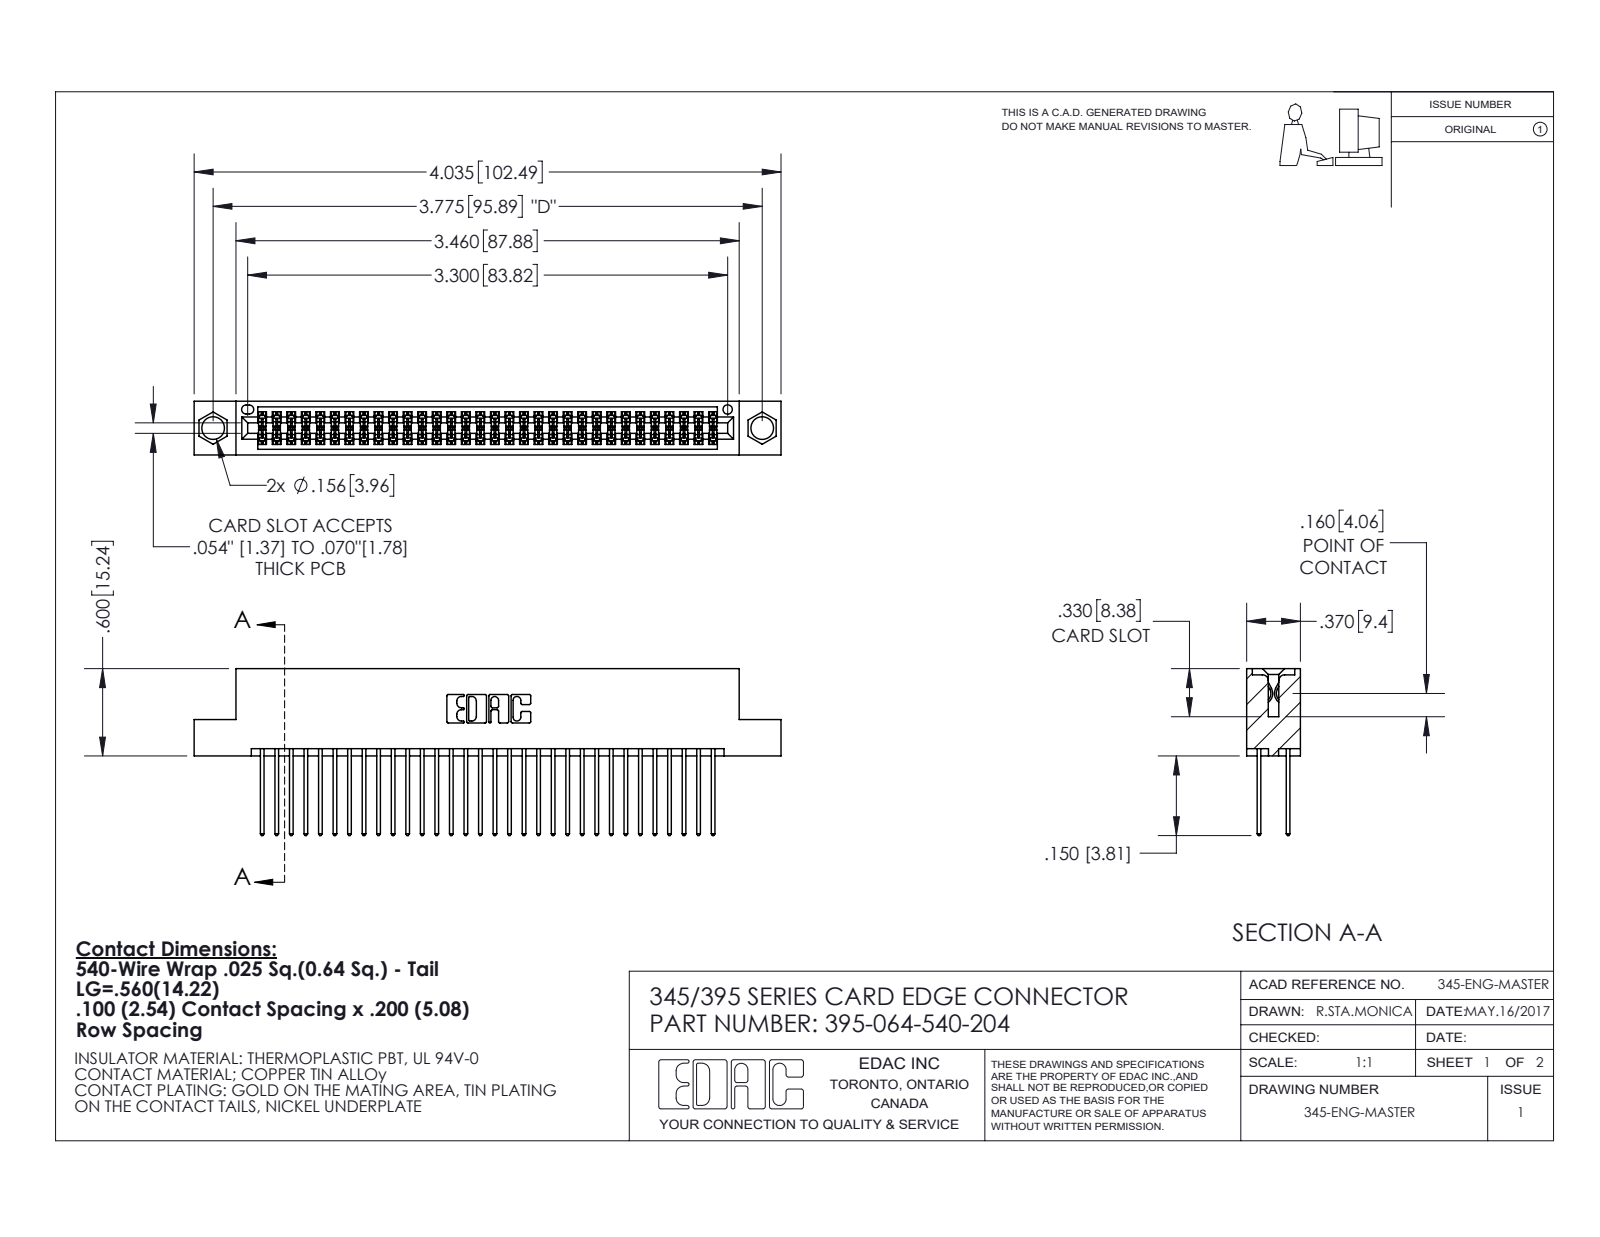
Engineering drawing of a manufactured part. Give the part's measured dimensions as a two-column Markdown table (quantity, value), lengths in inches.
| quantity | value |
| --- | --- |
| part name | 395-064-540-204; 345-292-001_345-293-140; 345 Part_Flush Mounting Lugs - 0.156 Dia-TI |
| STEP written by | SolidWorks 2020 (CONFIG_CONTROL_DESIGN) |
| units | inches |
| bodies | 65 solids, 3340 faces (2206 planar, 1134 cylindrical, 0 other) |
| overall size | 4.035 × 1.147 × 0.37 |
| volume | 0.61 in³ |
| surface area | 24.13 in² |
| round holes (diameter × count) | 0.156 × 2, 0.064 × 1 |
| partial cylindrical surfaces (radius × count) | 0.006 × 128, 0.01 × 64, 0.01 × 22, 0.007 × 6, 0.031 × 6, 0.026 × 3, 0.014 × 2, 0.019 × 2 |
| main face-to-face distances | 0.072, 0.298, 0.2, 0.098, 0.272, 0.025, 0.37, 0.225, 0.175, 0.149 |
| hole center spacings | 0.27, 3.54, 3.775 |
